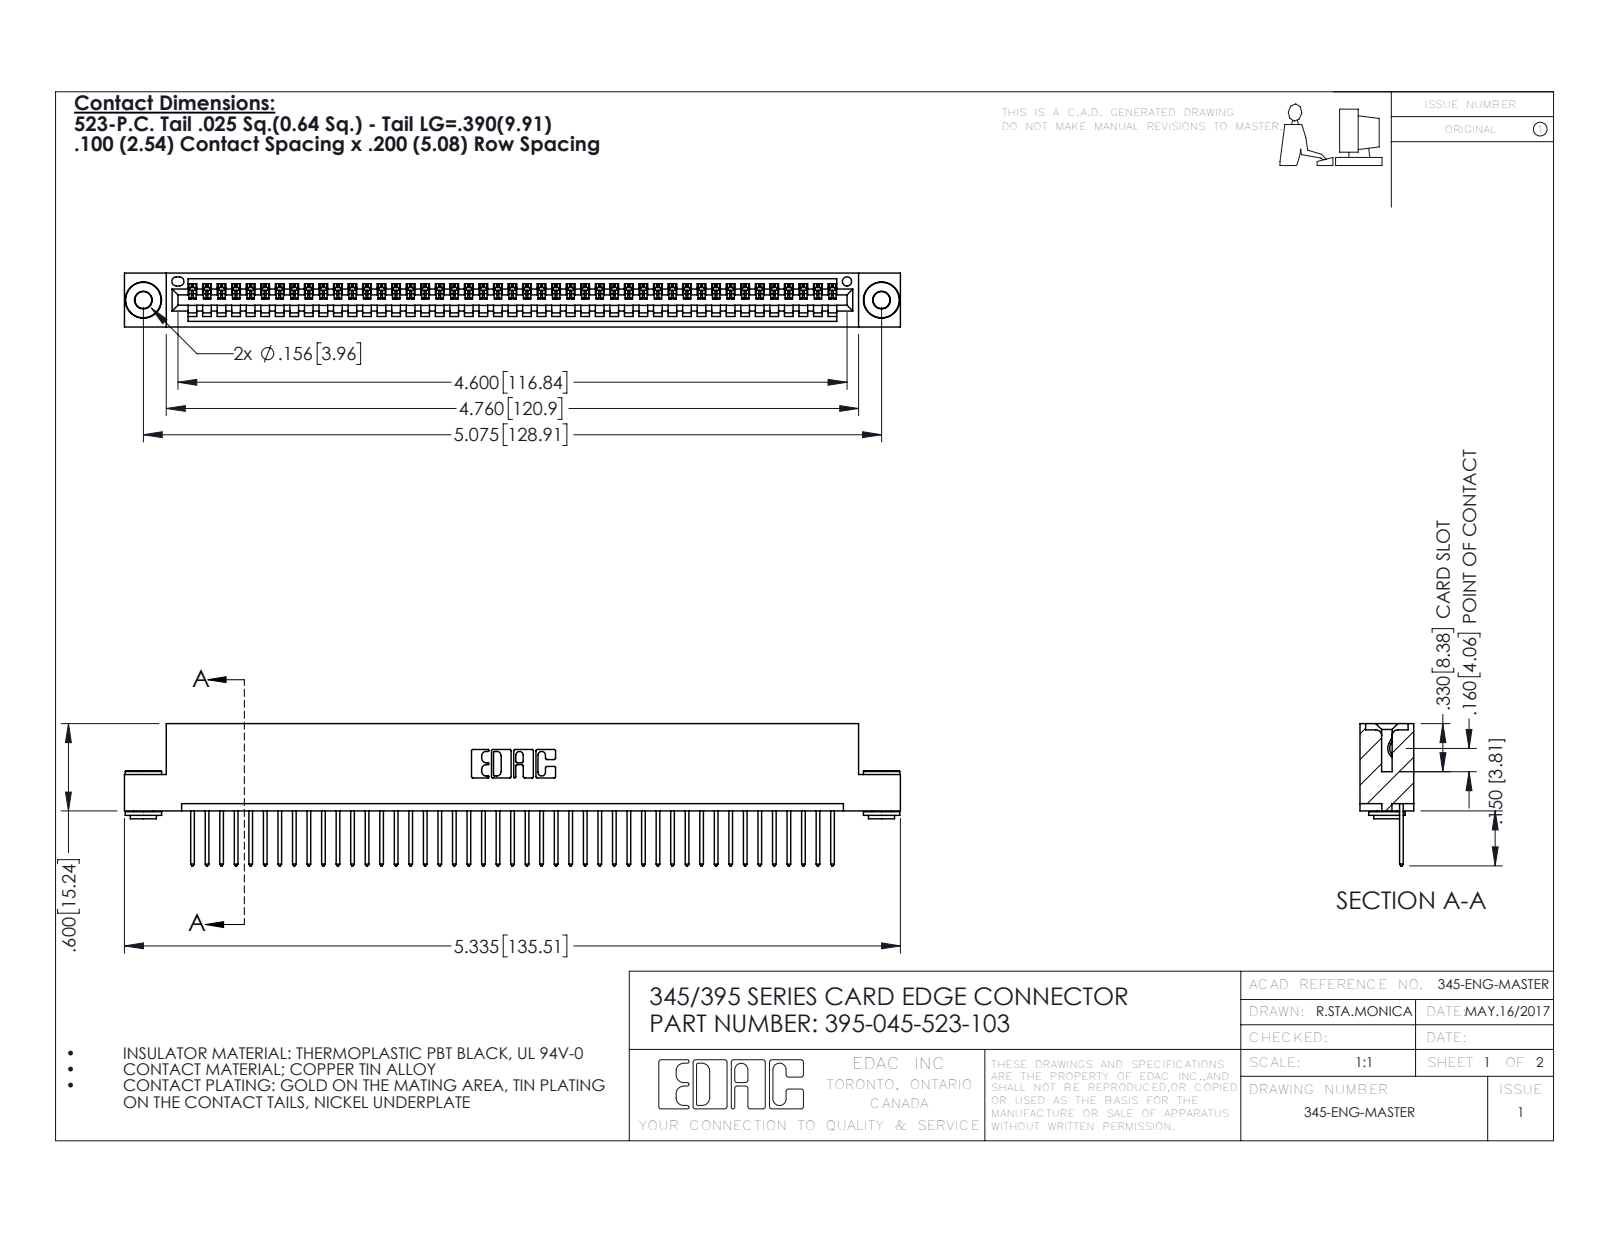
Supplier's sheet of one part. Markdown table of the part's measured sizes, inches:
| quantity | value |
| --- | --- |
| part name | 345-292-001_345-293-123; 395-045-523-103; 345 Part_Flush Mounting Lugs - 0.156 Dia-TH; 345-250-002_345-250-002-102 |
| STEP written by | SolidWorks 2016 (CONFIG_CONTROL_DESIGN) |
| units | inches |
| bodies | 48 solids, 2774 faces (1890 planar, 876 cylindrical, 8 other) |
| overall size | 5.335 × 0.977 × 0.37 |
| volume | 0.787 in³ |
| surface area | 27.04 in² |
| round holes (diameter × count) | 0.116 × 2, 0.156 × 2, 0.064 × 1 |
| round bosses / shafts (diameter × count) | 0.25 × 2, 0.18 × 2, 0.136 × 2 |
| partial cylindrical surfaces (radius × count) | 0.006 × 90, 0.01 × 90, 0.01 × 22, 0.007 × 6, 0.031 × 6, 0.026 × 3, 0.031 × 2, 0.04 × 2 |
| main face-to-face distances | 0.072, 0.298, 0.37, 0.2, 0.025, 0.098, 0.272, 0.225, 0.149, 0.072 |
| hole center spacings | 0.27, 4.839, 5.075 |
